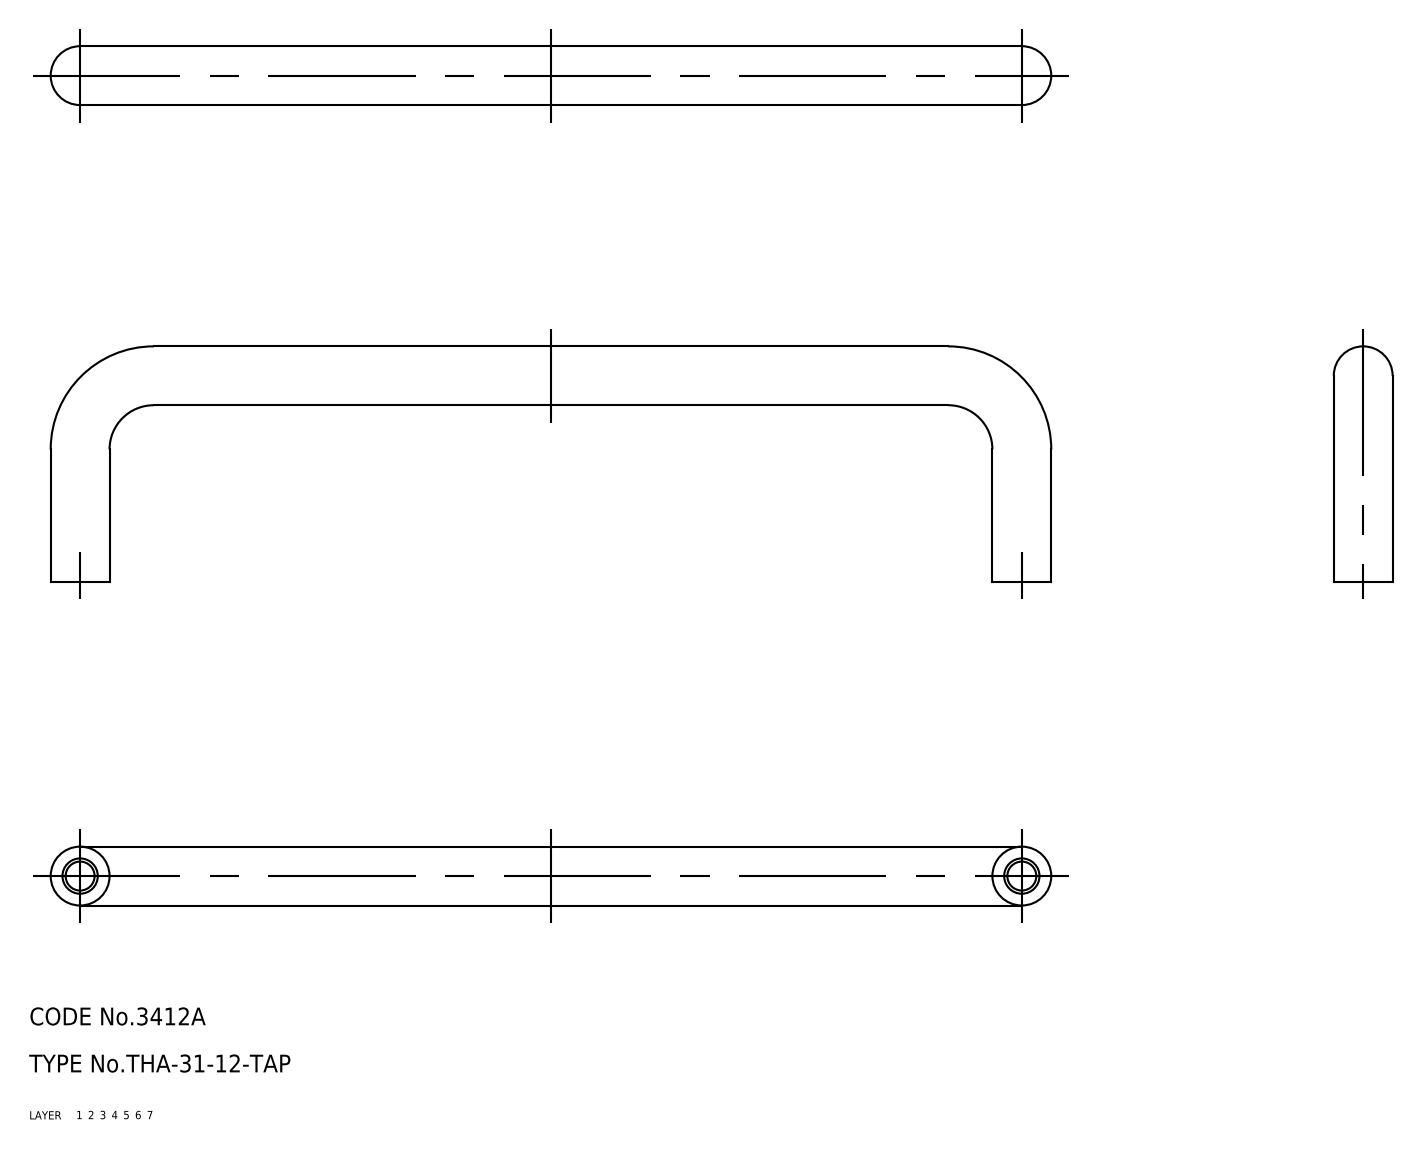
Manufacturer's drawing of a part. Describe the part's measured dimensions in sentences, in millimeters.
The part is named "pull". Its 3-D file was written by "CADfix (AUTOMOTIVE_DESIGN)". It is 1 solid with 18 faces: 0 planar, 0 cylindrical and 18 other. Overall it measures 170 by 40 by 10 millimeters. Its volume is 16 066 cubic millimeters and its surface area 7 804 square millimeters.
